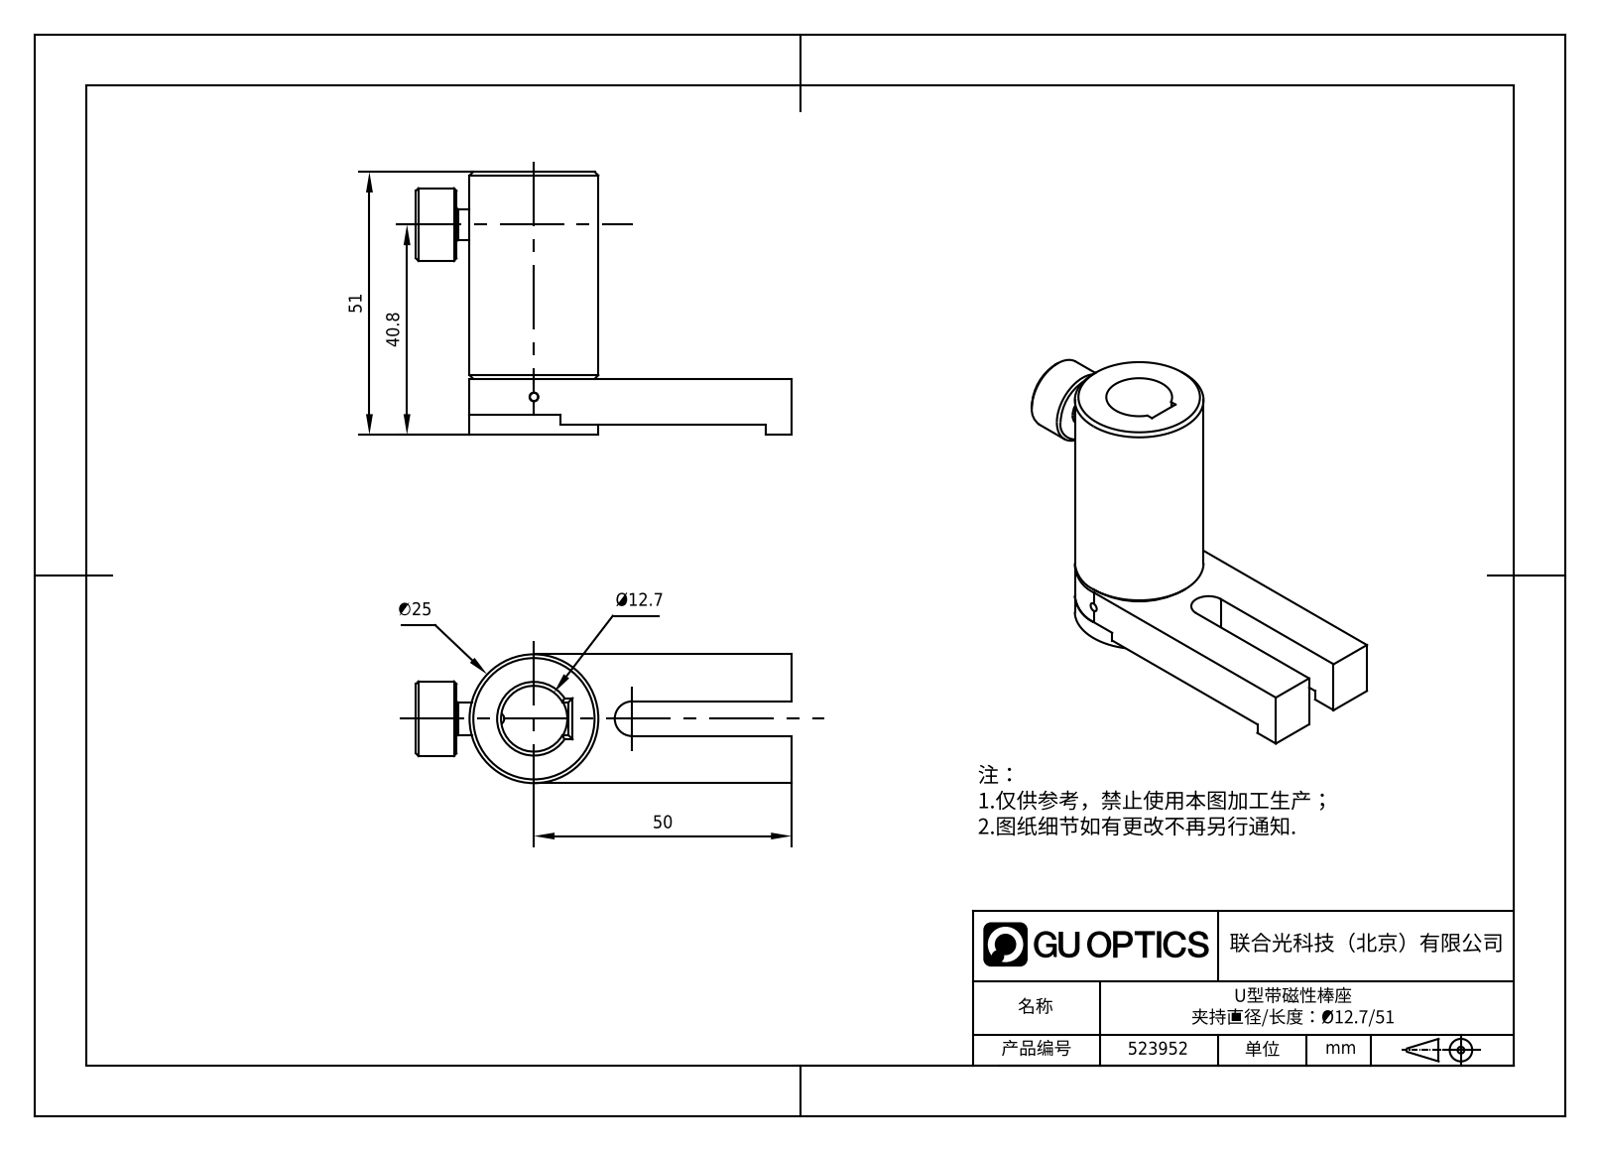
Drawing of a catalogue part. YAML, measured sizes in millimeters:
part_name: "523952"
step_written_by: "SolidWorks 2016 (CONFIG_CONTROL_DESIGN)"
units: millimeters
bodies: {solids: 8, faces: 128, planar: 38, cylindrical: 50, other: 40}
overall_size: [72.91, 51.05, 24.99]
volume: 27284
surface_area: 13748
round_holes:
  - {diameter: 4.83, count: 3}
  - {diameter: 1.59, count: 1}
  - {diameter: 1.7, count: 1}
  - {diameter: 1.78, count: 1}
  - {diameter: 12.78, count: 1}
  - {diameter: 12.95, count: 1}
  - {diameter: 20.09, count: 1}
round_bosses_or_shafts:
  - {diameter: 4.76, count: 3}
  - {diameter: 24.99, count: 1}
  - {diameter: 20.05, count: 1}
  - {diameter: 17.78, count: 1}
  - {diameter: 17.27, count: 1}
  - {diameter: 14.12, count: 1}
  - {diameter: 5.99, count: 1}
  - {diameter: 3, count: 1}
partial_cylinders:
  - {radius: 3.37, count: 1}
  - {radius: 12.95, count: 1}
face_to_face_distances: [8.89, 9.13, 15.87, 25, 1.83, 7.06, 1.98, 3.81, 10.87, 51]
hole_center_spacings: [16.5, 9.53, 9.52]
